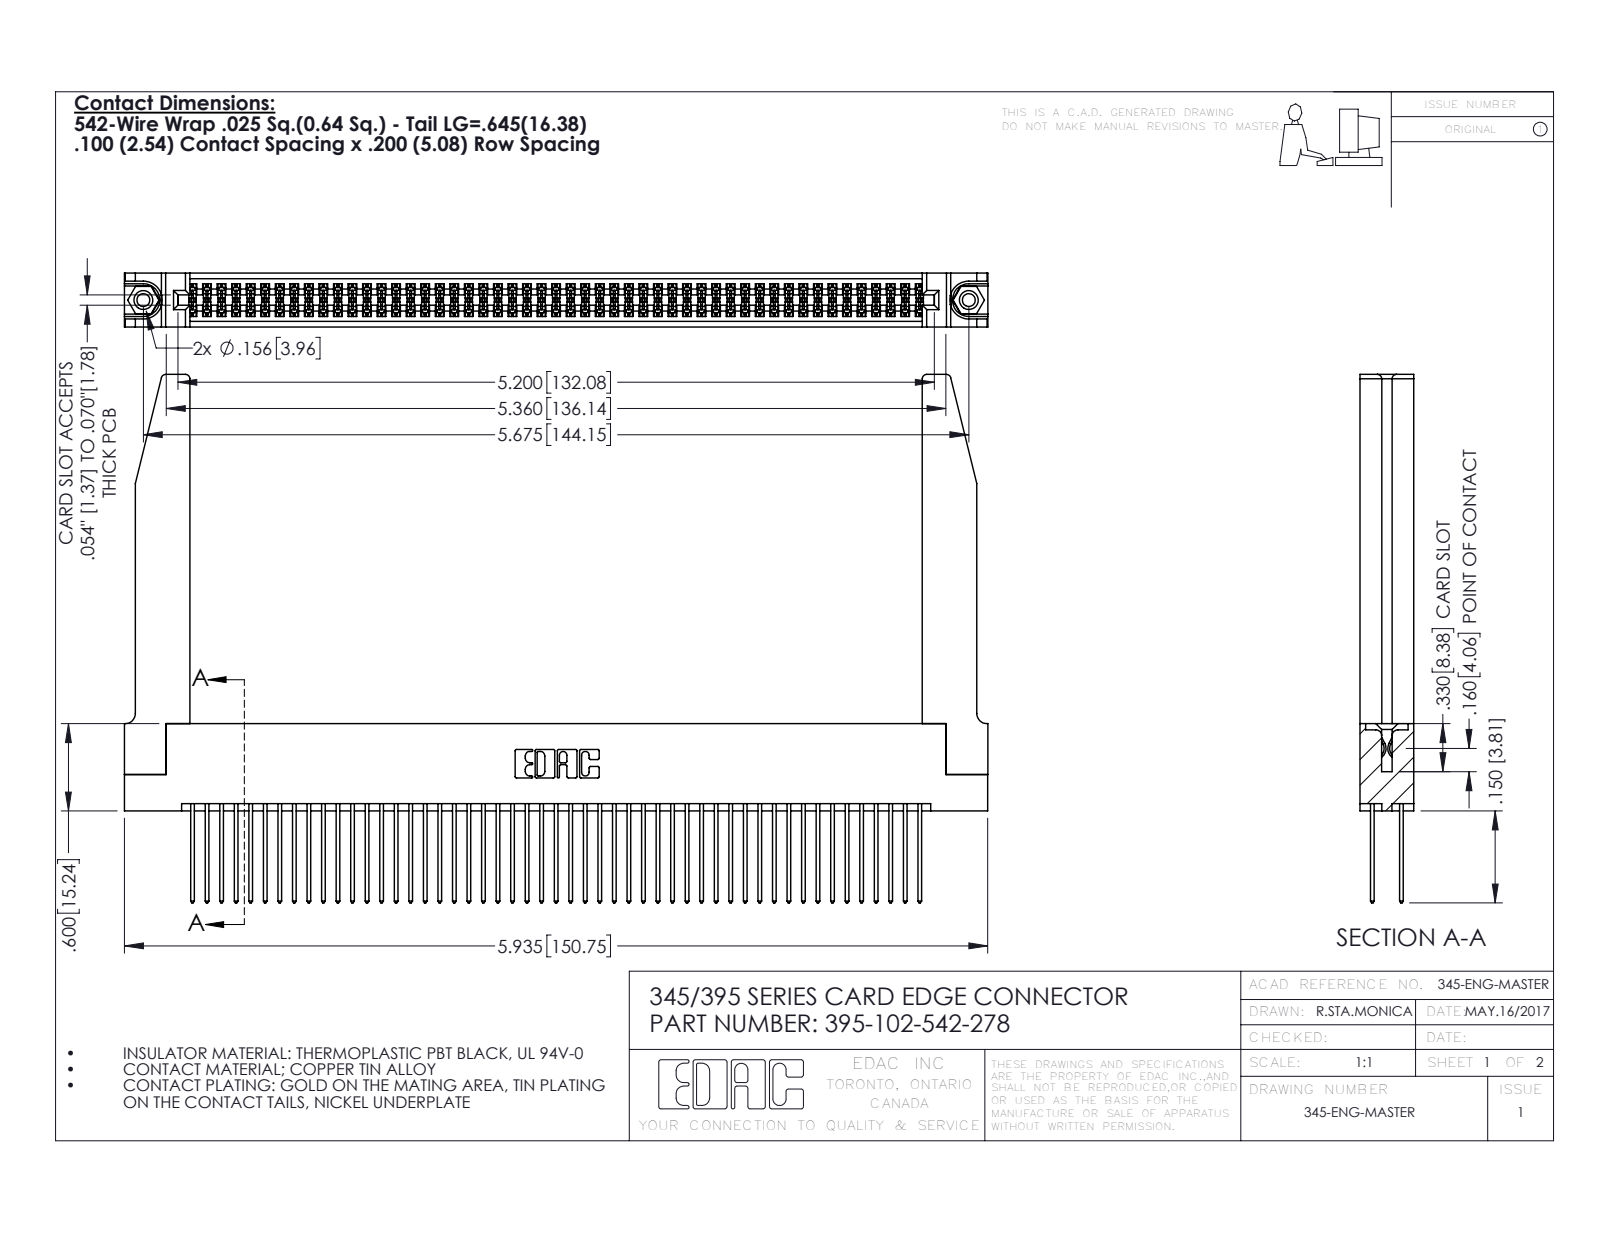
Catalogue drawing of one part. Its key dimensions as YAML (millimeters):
part_name: "345 Part_Flush Mounting Lugs - 0.156 Dia-TH; 345-220-078_345-220-078; 345-292-001_345-293-142; 345-250-001_345-250-001-102 (+1 more)"
step_written_by: "SolidWorks 2016 (CONFIG_CONTROL_DESIGN)"
units: millimeters
bodies: {solids: 107, faces: 5460, planar: 3588, cylindrical: 1820, other: 52}
overall_size: [150.8, 92.3, 9.4]
volume: 22970
surface_area: 31710
round_holes:
  - {diameter: 2.3, count: 2}
  - {diameter: 3.2, count: 2}
  - {diameter: 4, count: 2}
  - {diameter: 1.6, count: 1}
round_bosses_or_shafts:
  - {diameter: 3.9, count: 2}
partial_cylinders:
  - {radius: 0.2, count: 153}
  - {radius: 0.3, count: 102}
  - {radius: 0.3, count: 22}
  - {radius: 0.8, count: 8}
  - {radius: 0.2, count: 6}
  - {radius: 0.8, count: 6}
  - {radius: 0.7, count: 3}
  - {radius: 0.4, count: 2}
face_to_face_distances: [1.8, 7.6, 9.4, 5.1, 2.5, 6.9, 0.6, 5.7, 4.4, 3.8]
hole_center_spacings: [6.9, 138.2, 144.1]
